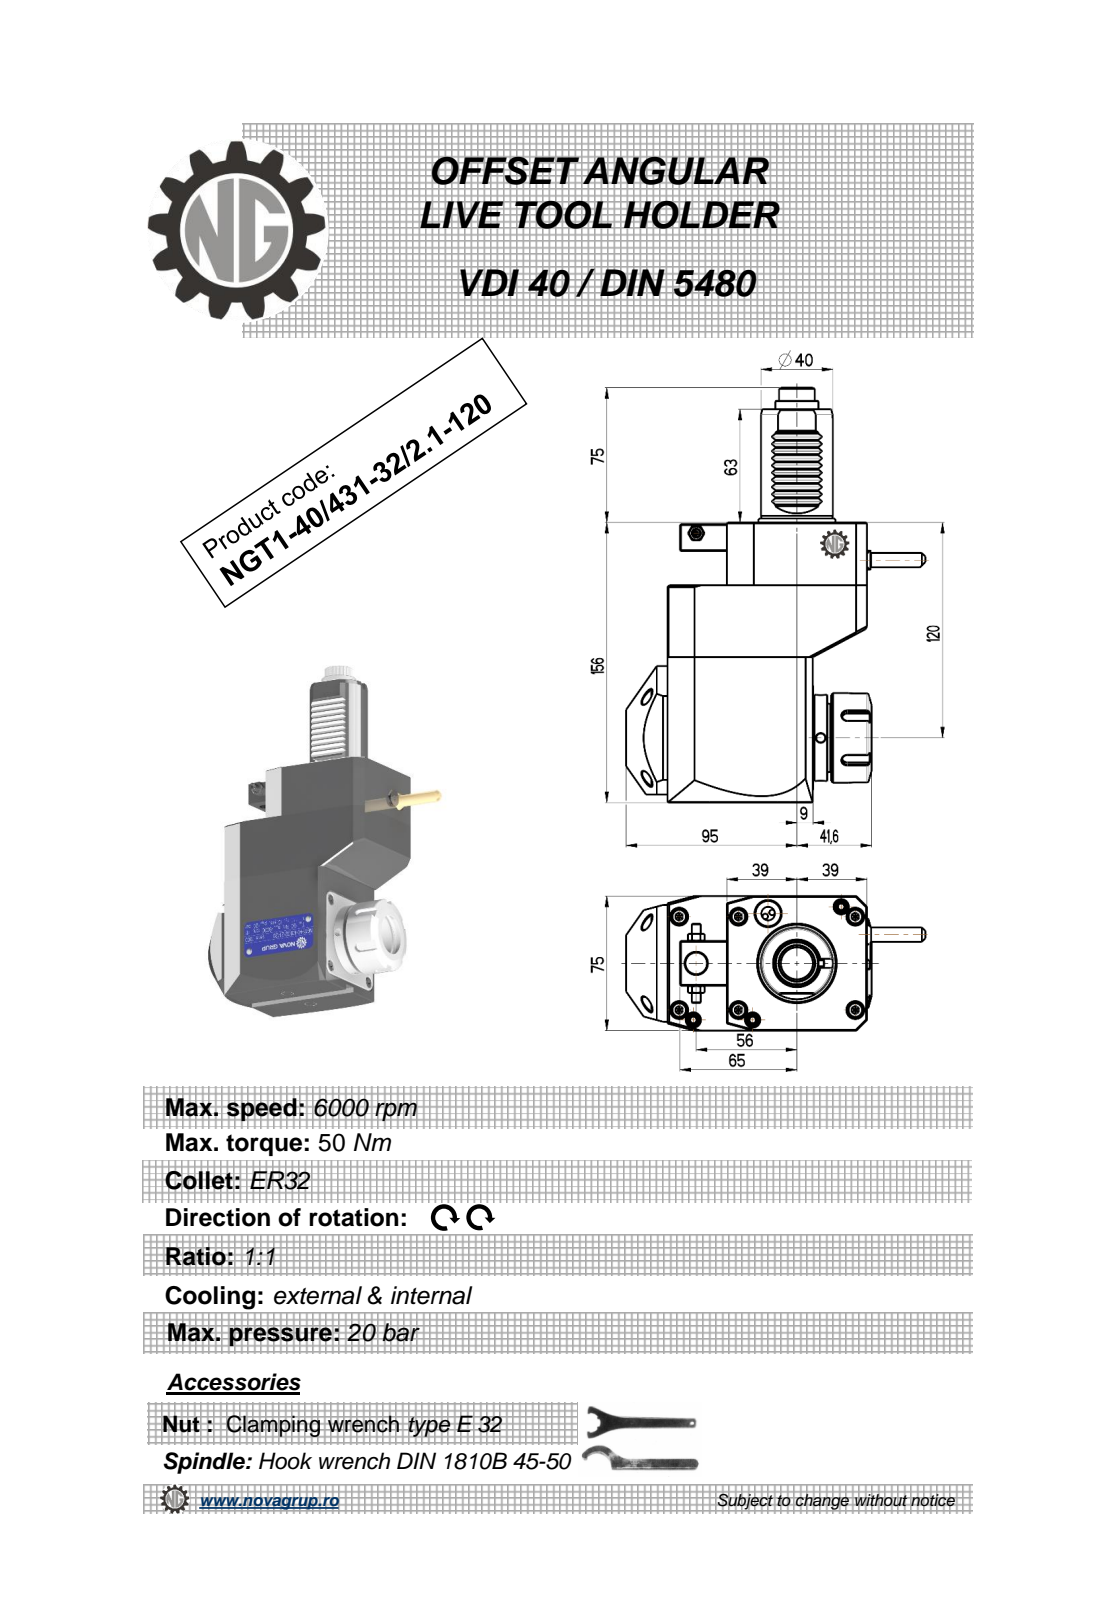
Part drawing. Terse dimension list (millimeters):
name: NGT1_40_431_32_2_1_120
written by: PRO/ENGINEER BY PARAMETRIC TECHNOLOGY CORPORATION, 2010280 (CONFIG_CONTROL_DESIGN)
unit: mm
bodies: 1 solid, 550 faces (211 planar, 185 cylindrical, 154 other)
size: 231 × 166.5 × 76.6
volume: 1 205 000 mm³; area: 88 503 mm²
holes: 3× ⌀5, 1× ⌀3, 1× ⌀4.2, 1× ⌀9.5, 1× ⌀12, 1× ⌀27
bosses: 1× ⌀50, 1× ⌀48, 1× ⌀41, 1× ⌀40, 1× ⌀24, 1× ⌀11.2, 1× ⌀8.96, 1× ⌀8
rounds: 48× R2.08, 12× R0.26, 10× R0.3, 6× R0.22, 5× R3, 1× R9.08, 1× R9.92, 1× R15
face distances: 75, 156, 111, 35, 30, 121, 81, 33, 48, 78
hole spacings: 20.3, 69.25, 100.28, 111.5, 133.39
